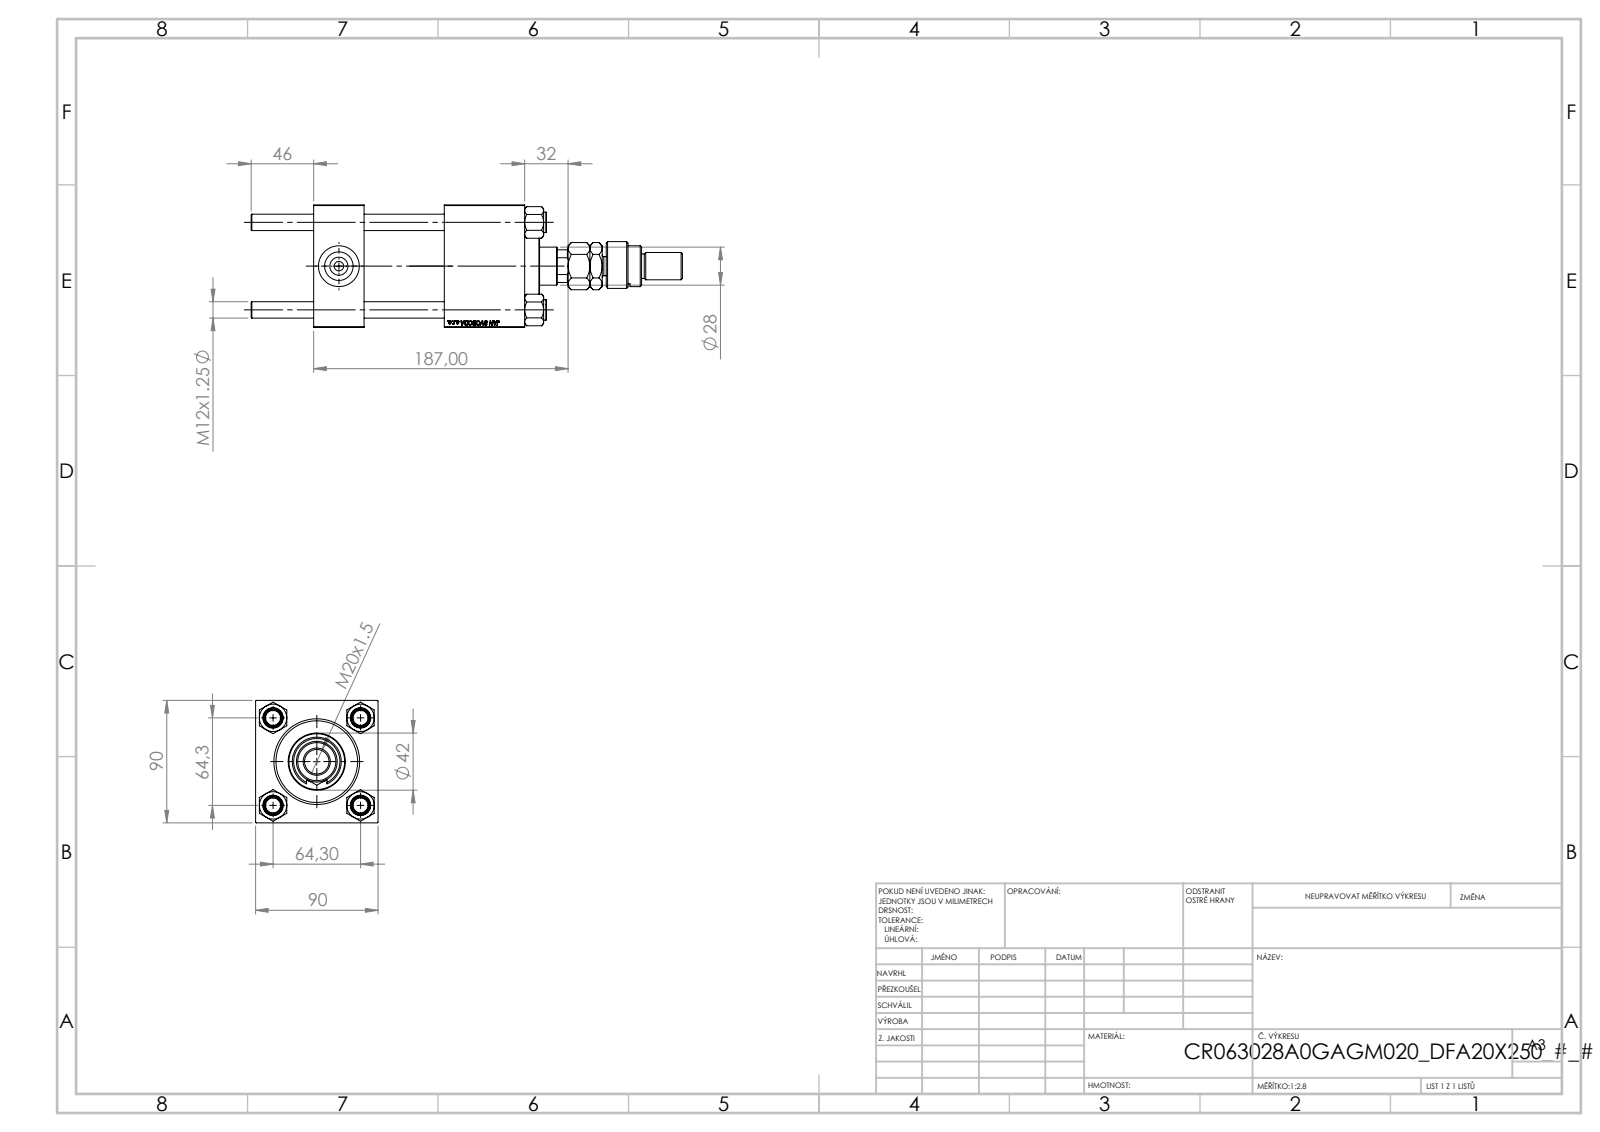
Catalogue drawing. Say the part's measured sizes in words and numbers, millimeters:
The part is named "MFA; V215CR_VCP; NUT_M5; CR025_012_A_0_G_A_G_M_020_+#_##_TYCINKA (+3 more)". Its 3-D file was written by "SolidWorks 2019 (CONFIG_CONTROL_DESIGN)". It is 13 solids with 1219 faces: 547 planar, 92 cylindrical and 580 other. Overall it measures 317 by 90 by 90 millimeters. Its volume is 1 029 000 cubic millimeters and its surface area 208 925 square millimeters. Round holes: 4 of diameter 12, 2 of diameter 7, 2 of diameter 20.96, 2 of diameter 30, 1 of diameter 18.5, 1 of diameter 28, 1 of diameter 31, 1 of diameter 50, 1 of diameter 60, 1 of diameter 63. Round bosses or shafts: 4 of diameter 15, 1 of diameter 69, 1 of diameter 42, 1 of diameter 36, 1 of diameter 30, 1 of diameter 22, 1 of diameter 20, 1 of diameter 18. Partial cylindrical surfaces (rounded edges, fillets, slot ends): 1 of radius 7.5, 1 of radius 12, 1 of radius 13.5. The main face-to-face distances are 90, 59, 37, 155, 118, 96, 126.3, 89.3, 30.3, 28.7. The hole center spacings are 45.47, 64.3, 90.93.
